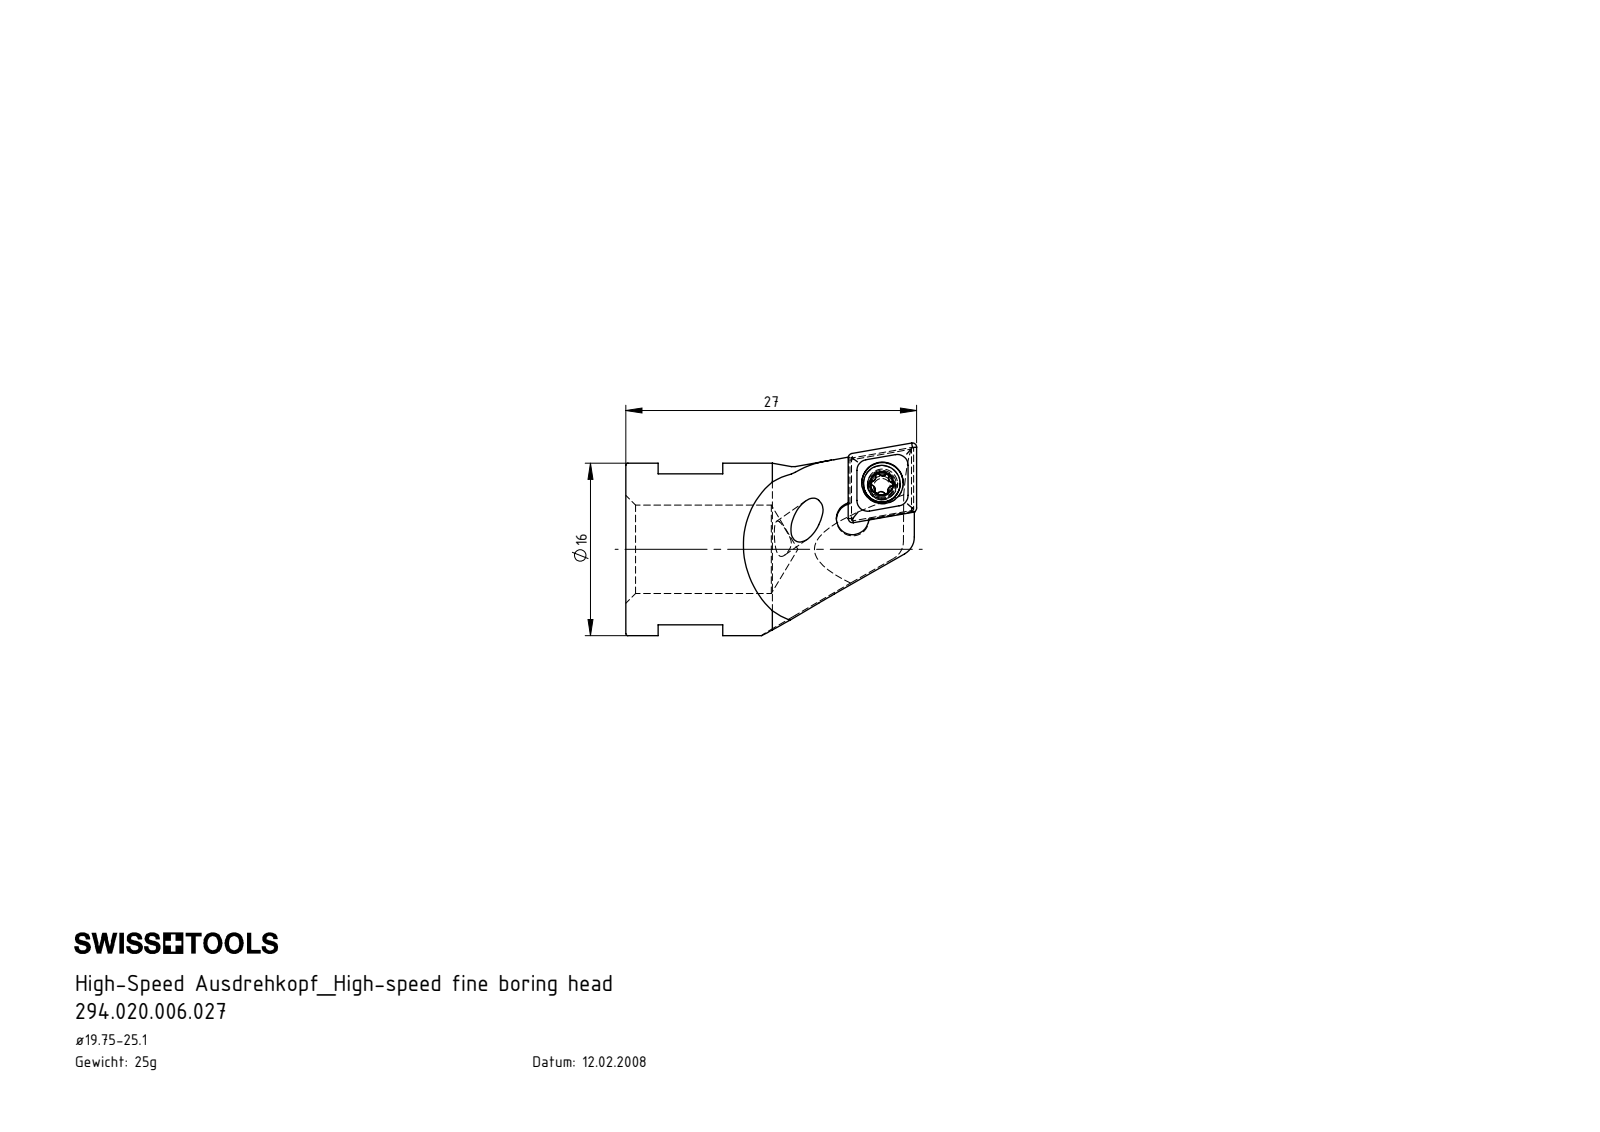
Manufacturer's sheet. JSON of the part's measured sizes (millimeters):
{"part_name": "WCA-ER2.001.006_A; HS0-A20.K11.027_B; HS0.A20.K11.027; CCMT060204", "step_written_by": "SolidWorks 2017 (AUTOMOTIVE_DESIGN)", "units": "millimeters", "bodies": {"solids": 3, "faces": 123, "planar": 34, "cylindrical": 35, "other": 54}, "overall_size": [27, 17.88, 16], "volume_mm3": 3115, "surface_area_mm2": 2094, "round_holes": [[2.05, 1], [2.8, 1], [3, 1], [3.85, 1], [8.2, 1]], "round_bosses_or_shafts": [[16, 1], [3.4, 1], [2.5, 1]], "partial_cylinders_radius": [[0.21, 6], [0.36, 5], [0.36, 1], [1.5, 1], [1.8, 1], [2, 1]], "face_to_face_distances": [14, 2.29, 6, 9, 3, 2.38, 20.8, 17.8, 11.8, 1.75]}
